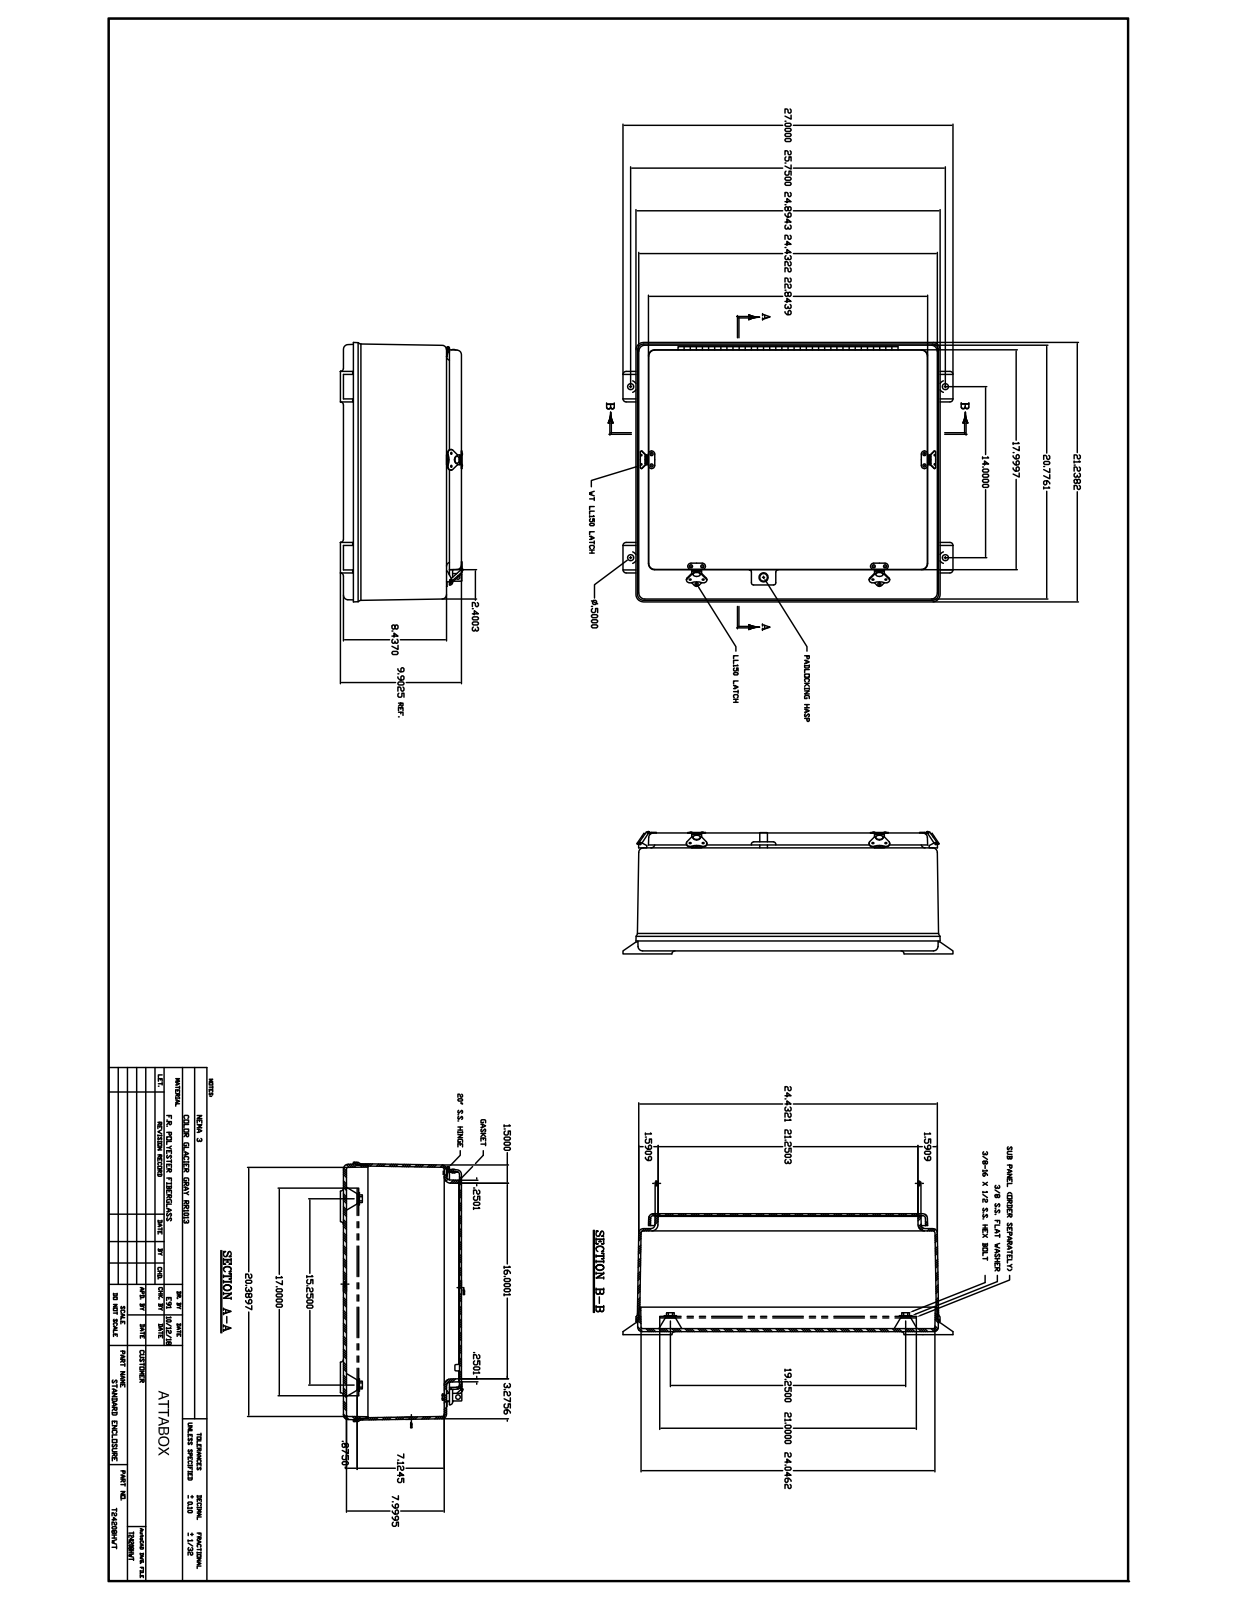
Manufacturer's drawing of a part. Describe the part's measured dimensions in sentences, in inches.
The part is named "T24208HWT". Its 3-D file was written by "SolidWorks 2018 (AUTOMOTIVE_DESIGN)". It is 56 solids with 1502 faces: 567 planar, 594 cylindrical and 341 other. Overall it measures 27 by 21.25 by 10.239 inches. Its volume is 410.2 cubic inches and its surface area 4 352 square inches. Round holes: 34 of diameter 0.13, 16 of diameter 0.063, 8 of diameter 0.138, 8 of diameter 0.187, 6 of diameter 0.065, 4 of diameter 0.281, 4 of diameter 0.563, 3 of diameter 0.135, 3 of diameter 0.156, 2 of diameter 0.065, 2 of diameter 0.145, 2 of diameter 0.51. Round bosses or shafts: 16 of diameter 0.14, 8 of diameter 0.297, 4 of diameter 0.5, 3 of diameter 0.2, 3 of diameter 0.135, 1 of diameter 0.25, 1 of diameter 0.201. Partial cylindrical surfaces (rounded edges, fillets, slot ends): 101 of radius 0.01, 24 of radius 0.25, 16 of radius 0.03, 16 of radius 0.375, 13 of radius 0.187, 12 of radius 0.5, 10 of radius 0.125, 9 of radius 0.312. The main face-to-face distances are 0.25, 0.186, 9.657, 9.407, 9.5, 9.25, 0.156, 8.436, 8.25, 8. The hole center spacings are 0.5, 5.25, 0.937, 1, 1.453, 3.309, 11.75, 14.938.
